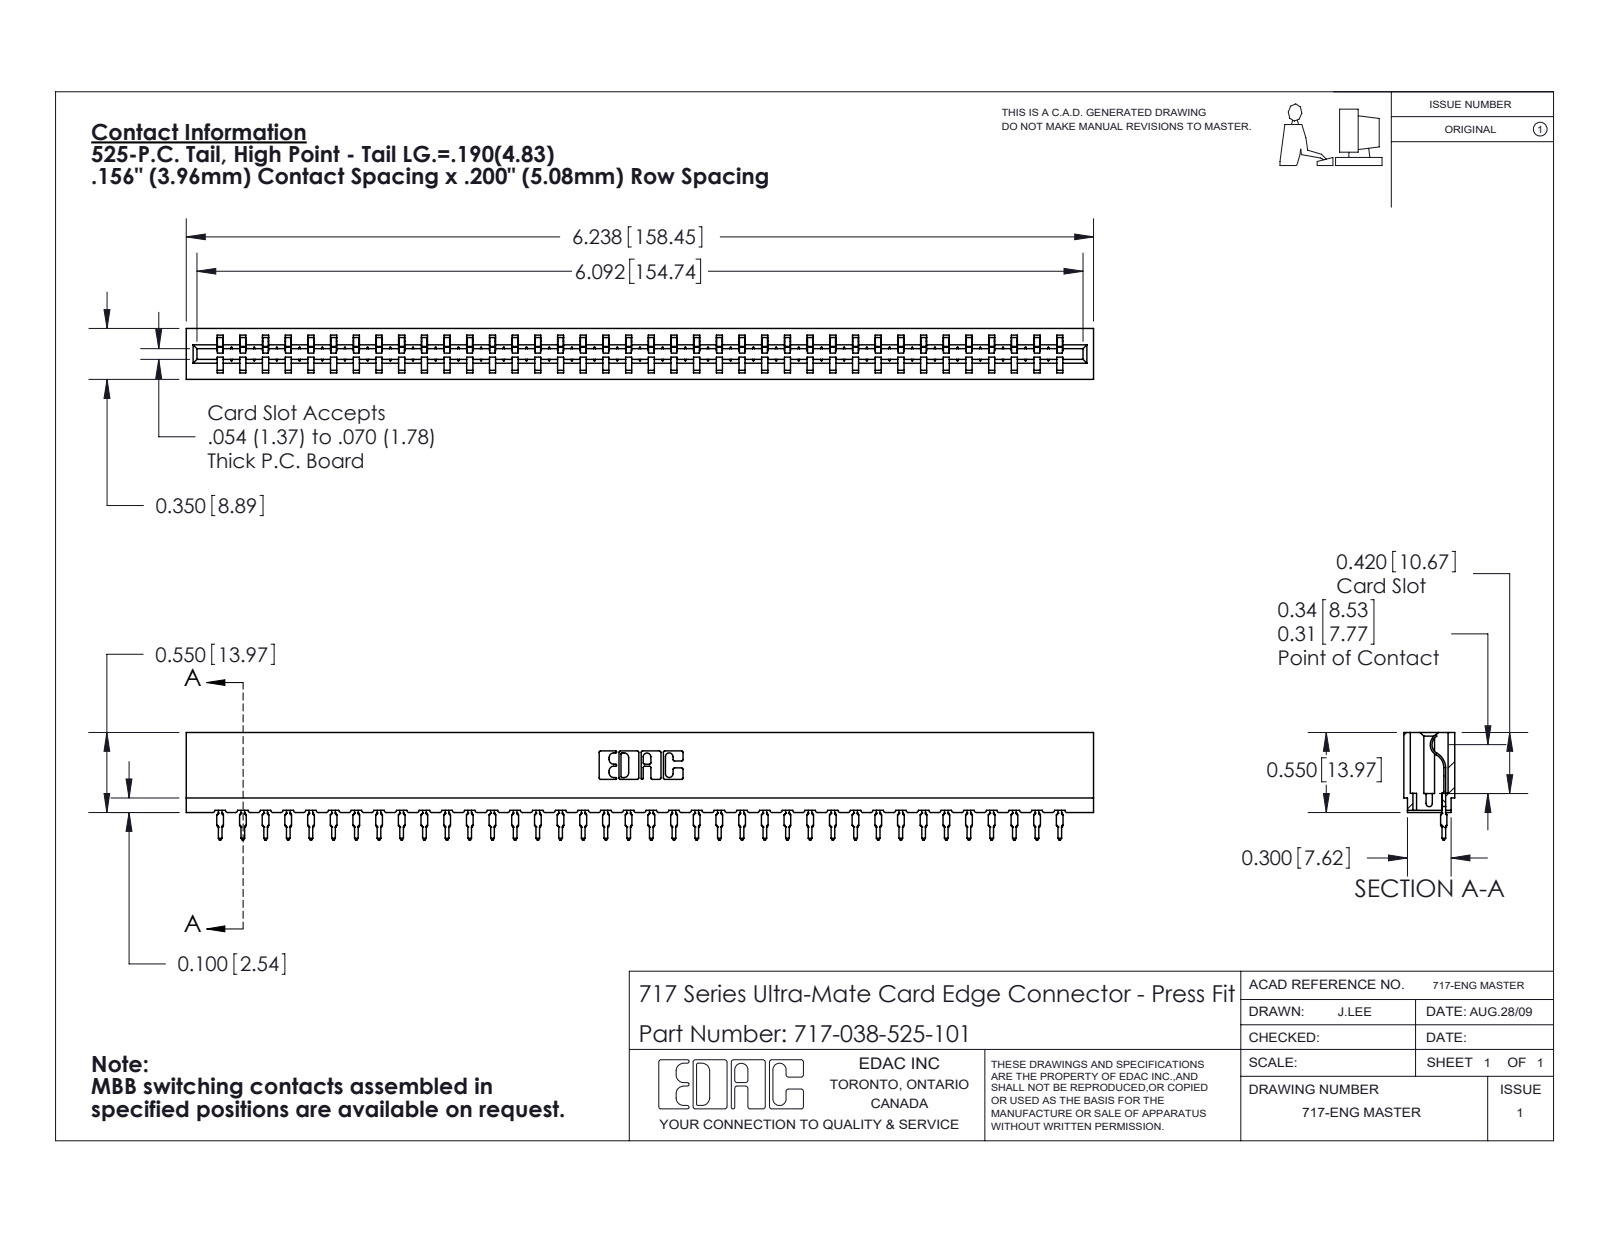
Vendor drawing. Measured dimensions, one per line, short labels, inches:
name: 717-038-525-101; 745-292-001_525; 717 Part_Insulator Option - 06
written by: SolidWorks 2020 (CONFIG_CONTROL_DESIGN)
unit: in
bodies: 39 solids, 4388 faces (2638 planar, 762 cylindrical, 988 other)
size: 6.238 × 0.739 × 0.35
volume: 0.815 in³; area: 28.85 in²
rounds: 76× R0.015, 76× R0.021, 22× R0.01, 6× R0.007, 6× R0.031, 4× R0.005, 4× R0.011, 3× R0.026
face distances: 0.212, 0.138, 0.35, 0.074, 0.045, 0.305, 0.093, 0.167, 0.025, 0.063
